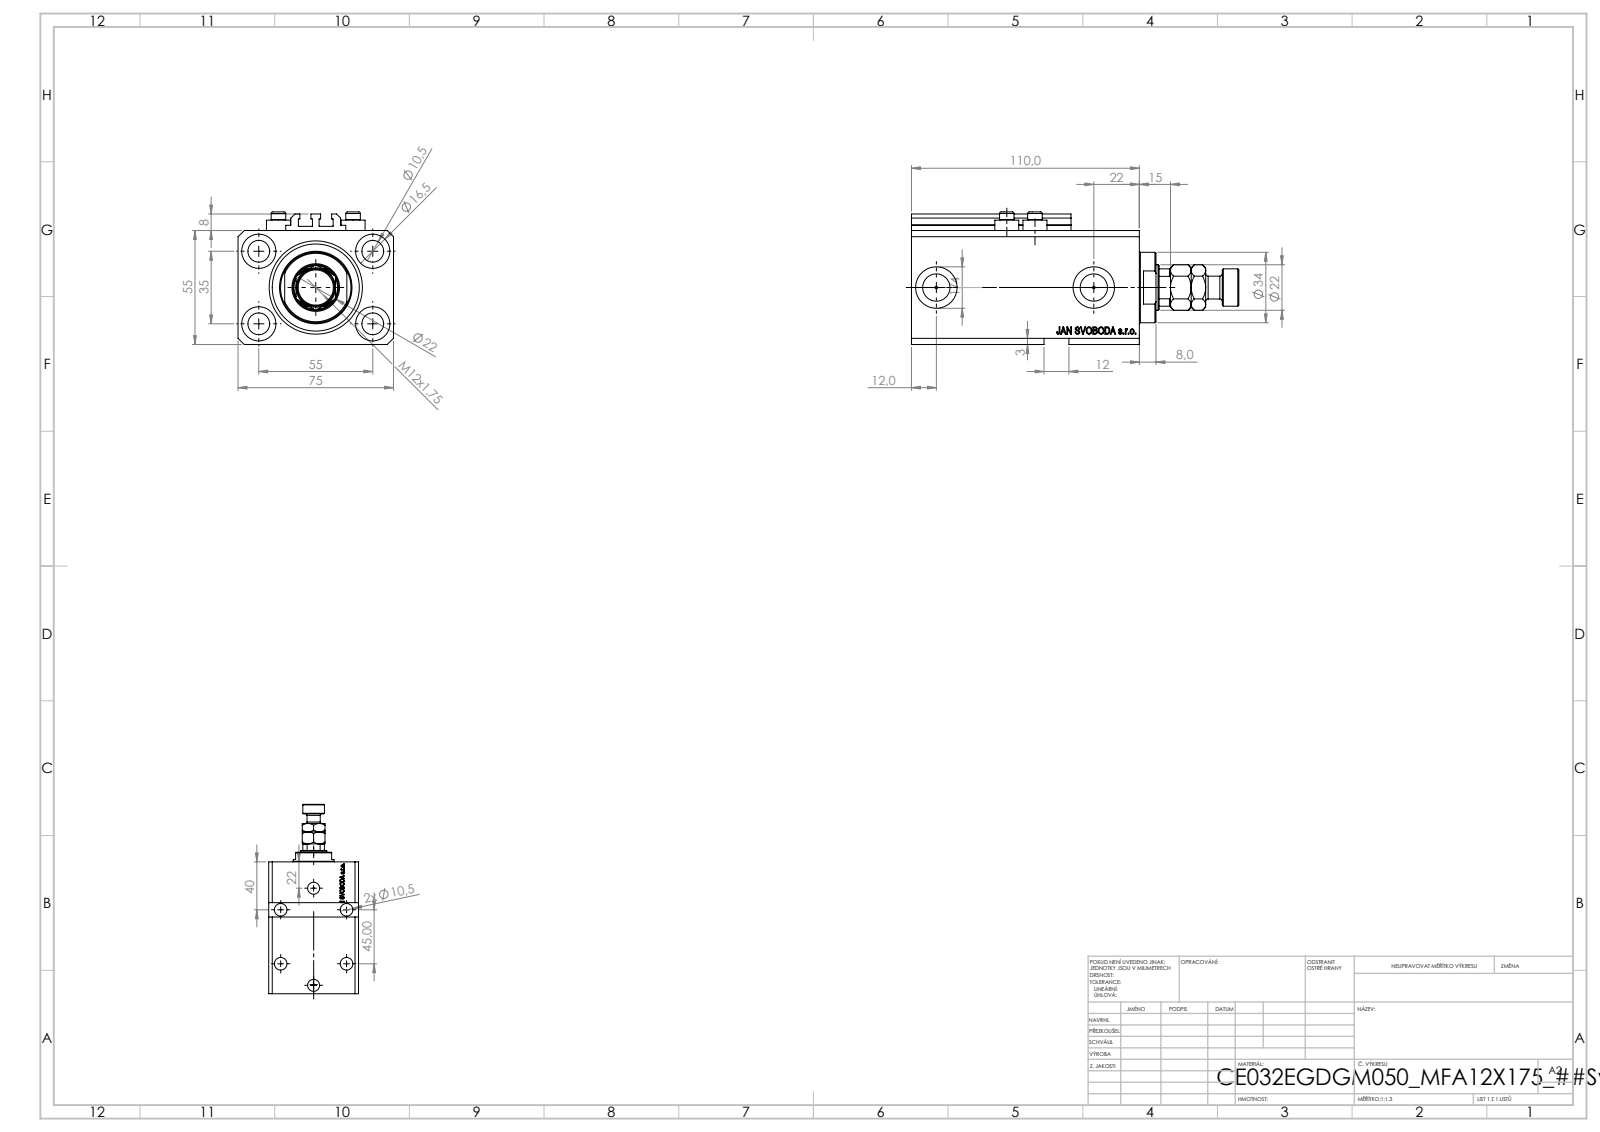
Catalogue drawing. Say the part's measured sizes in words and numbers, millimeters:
The part is named "ALLEN BOLT V250CE; V250CE_E_Body; V250CE_C_VCP; V250CE_VC_E (+1 more)". Its 3-D file was written by "SolidWorks 2019 (CONFIG_CONTROL_DESIGN)". It is 9 solids with 1152 faces: 534 planar, 162 cylindrical and 456 other. Overall it measures 158 by 75 by 64 millimeters. Its volume is 385 785 cubic millimeters and its surface area 99 488 square millimeters. Round holes: 9 of diameter 10.5, 4 of diameter 1.25, 4 of diameter 4, 4 of diameter 16.5, 2 of diameter 10, 2 of diameter 13.16, 2 of diameter 20, 1 of diameter 22, 1 of diameter 32, 1 of diameter 45. Round bosses or shafts: 4 of diameter 11.6, 4 of diameter 7, 1 of diameter 34, 1 of diameter 18, 1 of diameter 11. Partial cylindrical surfaces (rounded edges, fillets, slot ends): 10 of radius 0.2, 1 of radius 10.5. The main face-to-face distances are 55, 75, 15, 110, 95, 9.9, 3, 85.1, 100.1, 2.5. The hole center spacings are 32.6, 32.87, 55, 68.74, 13.6, 14.09, 23.05, 25.81.
